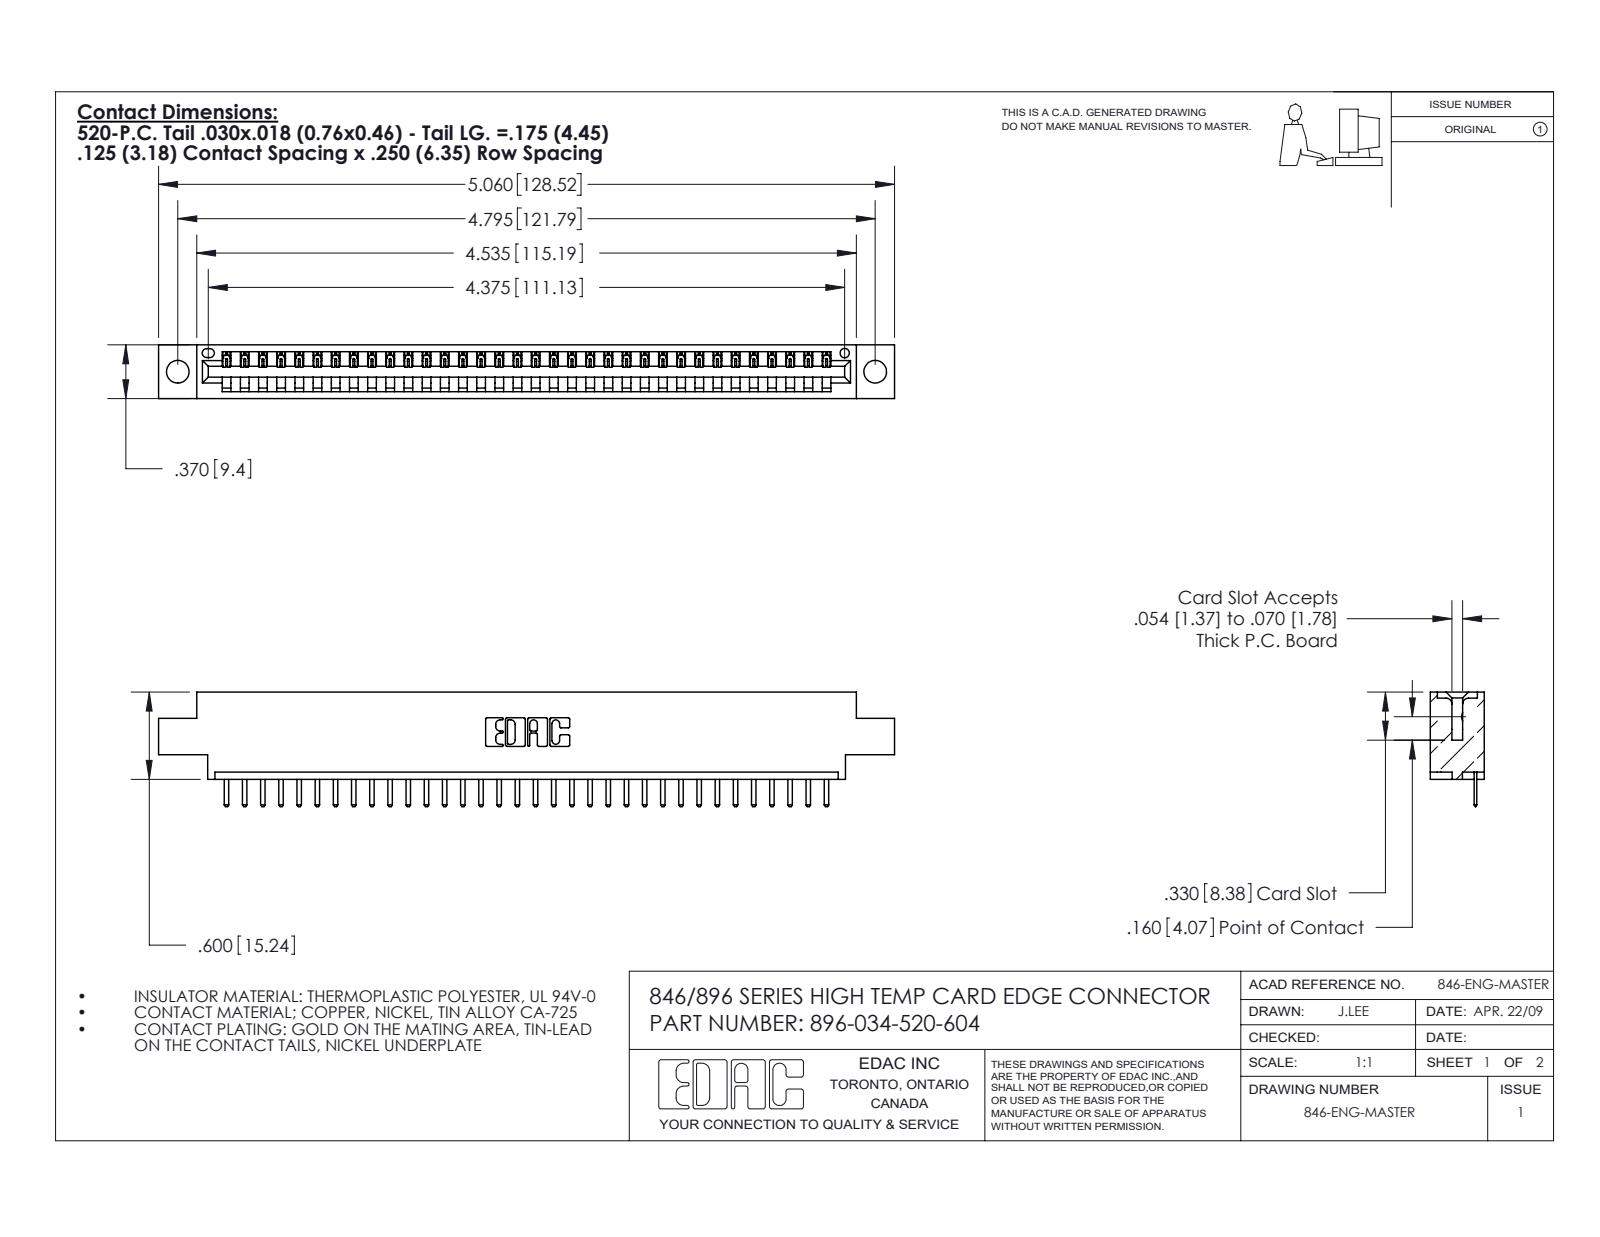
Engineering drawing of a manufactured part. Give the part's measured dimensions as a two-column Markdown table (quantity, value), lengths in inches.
| quantity | value |
| --- | --- |
| part name | 396-034-520-604; 345-292-001_345-293-120; 346 Part_0.170 Offset - 0.156 Dia-TH |
| STEP written by | SolidWorks 2016 (CONFIG_CONTROL_DESIGN) |
| units | inches |
| bodies | 35 solids, 2234 faces (1508 planar, 726 cylindrical, 0 other) |
| overall size | 5.06 × 0.788 × 0.37 |
| volume | 0.727 in³ |
| surface area | 22.37 in² |
| round holes (diameter × count) | 0.156 × 2, 0.064 × 1 |
| partial cylindrical surfaces (radius × count) | 0.01 × 70, 0.006 × 68, 0.01 × 22, 0.007 × 6, 0.031 × 6, 0.026 × 3, 0.031 × 2, 0.04 × 2 |
| main face-to-face distances | 0.048, 0.322, 0.37, 0.25, 0.148, 0.222, 0.1, 0.174, 0.072, 0.298 |
| hole center spacings | 0.246, 4.587, 4.795 |
